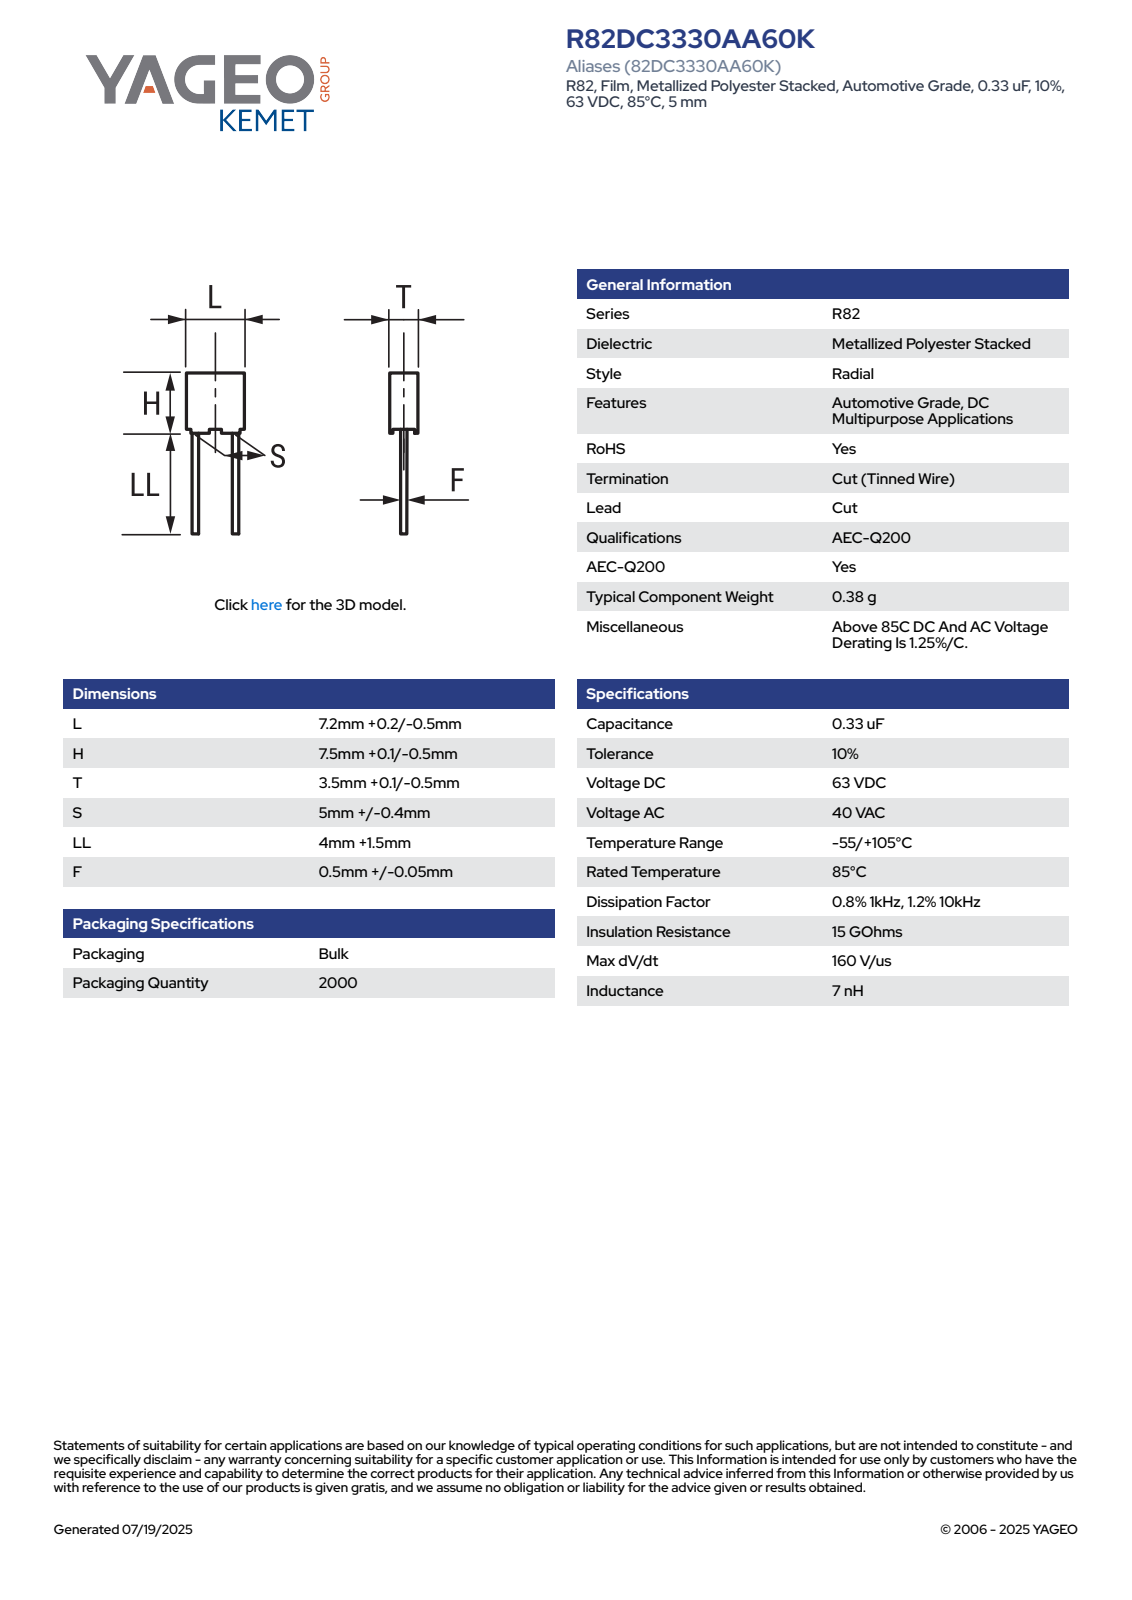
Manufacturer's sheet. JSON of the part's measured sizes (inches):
{"part_name": "CFR_RB3_7.2X7.5X3.5_L7.4H7.6T3.6S5LL5.5F0.55", "step_written_by": "SolidWorks 2014 (AUTOMOTIVE_DESIGN)", "units": "inches", "bodies": {"solids": 4, "faces": 85, "planar": 77, "cylindrical": 8, "other": 0}, "overall_size": [0.516, 0.291, 0.142], "volume_in3": 0.011, "surface_area_in2": 0.395, "round_bosses_or_shafts": [[0.022, 2]], "partial_cylinders_radius": [[0.02, 4]], "face_to_face_distances": [0.142, 0.291, 0.27, 0.132, 0.122, 0.281, 0.03, 0.299, 0.272, 0.019]}
